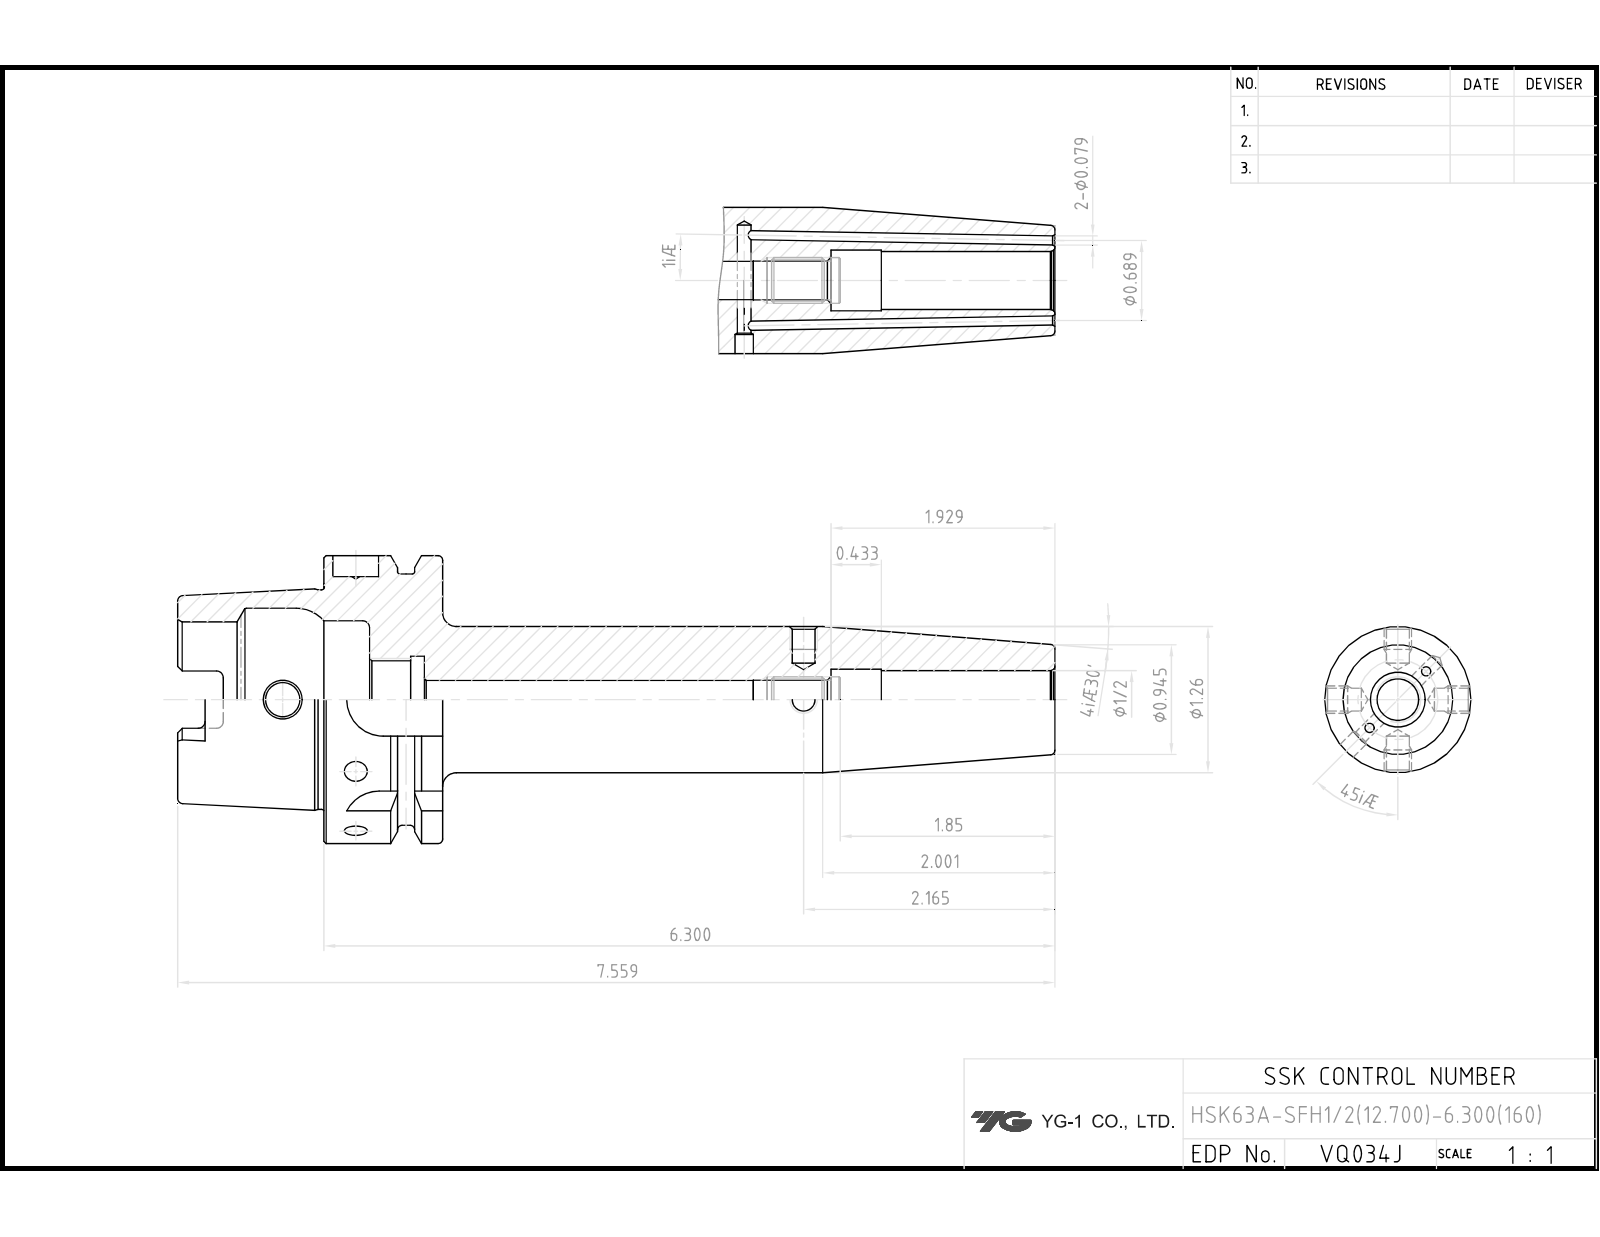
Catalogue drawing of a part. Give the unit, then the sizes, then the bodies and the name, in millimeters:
Units: millimetres
Overall size (bounding box): 192 × 63 × 63
Round holes (diameter × count): ⌀2 ×2, ⌀5 ×2, ⌀6 ×2, ⌀10 ×2, ⌀7.5 ×1, ⌀8.4 ×1, ⌀9 ×1, ⌀12.7 ×1, ⌀13.3 ×1, ⌀17 ×1, ⌀18 ×1, ⌀19 ×1
Round bosses / shafts (diameter × count): ⌀63 ×1, ⌀55 ×1, ⌀48.04 ×1, ⌀32 ×1
Partial cylindrical surfaces — rounded edges, fillets, slot ends (radius × count): R1.5 ×6, R2.88 ×4, R8 ×4
Main face-to-face distances: 26, 10, 16, 32, 6.12, 9.88, 42, 58, 4, 22
Hole centre spacings: 98, 114
Volume: 167 666 mm³ · Surface area: 41 629 mm²
Bodies: 1 solid, 206 faces (63 planar, 73 cylindrical, 70 other)
Part name (STEP PRODUCT): VQ034J-HSK63A-SFH0_5-6_30
STEP written by: CREO PARAMETRIC BY PTC INC, 2018100 (CONFIG_CONTROL_DESIGN)
